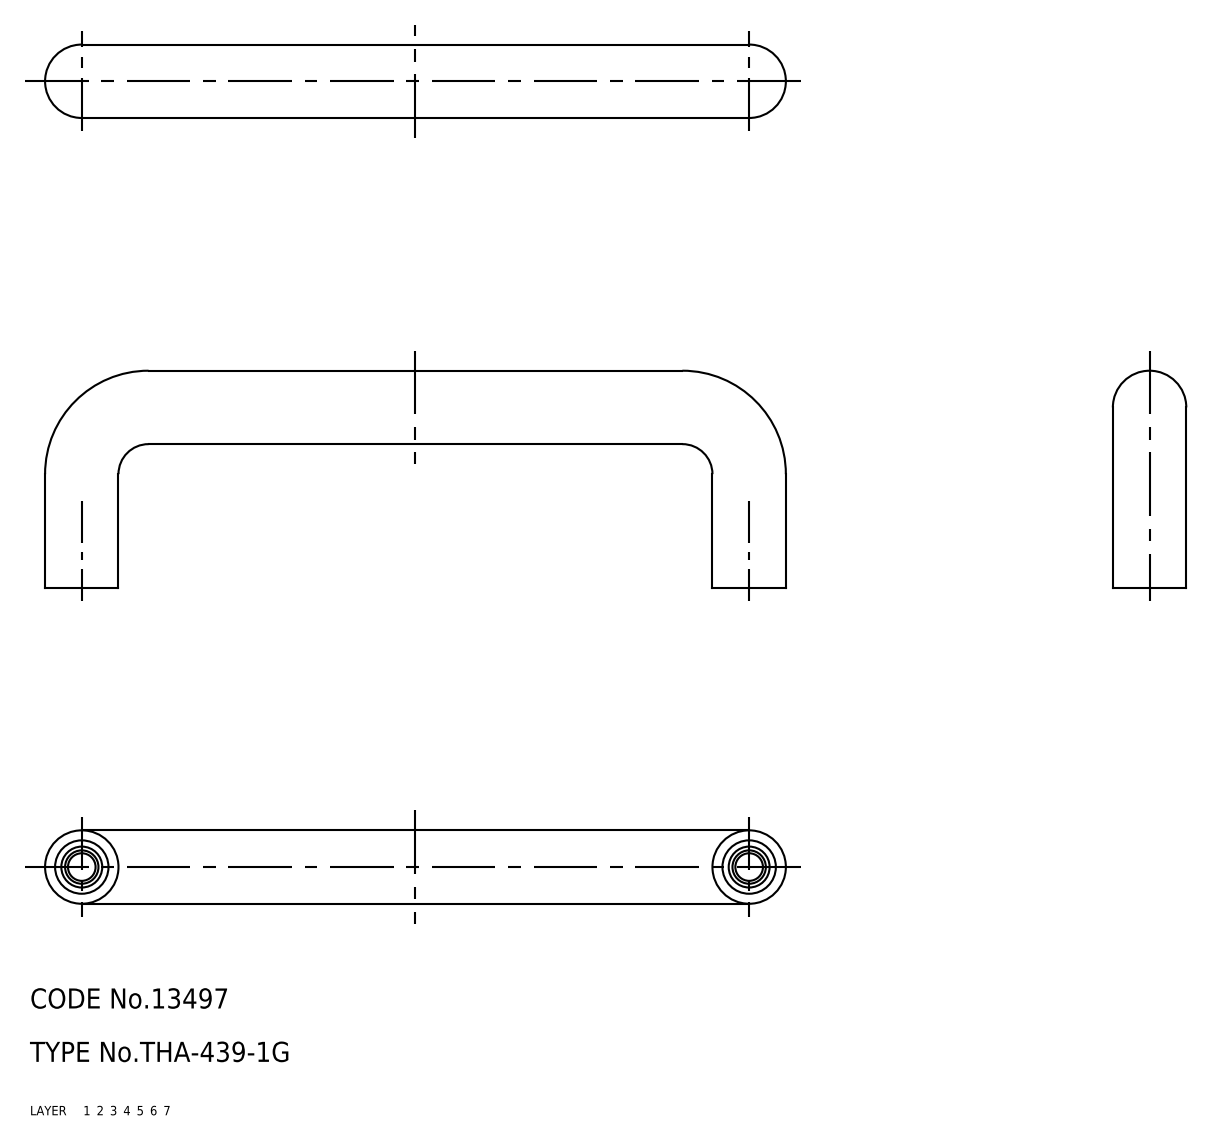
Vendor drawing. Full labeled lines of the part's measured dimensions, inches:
Part name (STEP PRODUCT): 67111903; 67111916
STEP written by: CADfix (AUTOMOTIVE_DESIGN)
Units: inches
Bodies: 2 solids, 40 faces (0 planar, 0 cylindrical, 40 other)
Overall size (bounding box): 4.37 × 1.28 × 0.433
Volume: 0.813 in³ · Surface area: 20.07 in²
